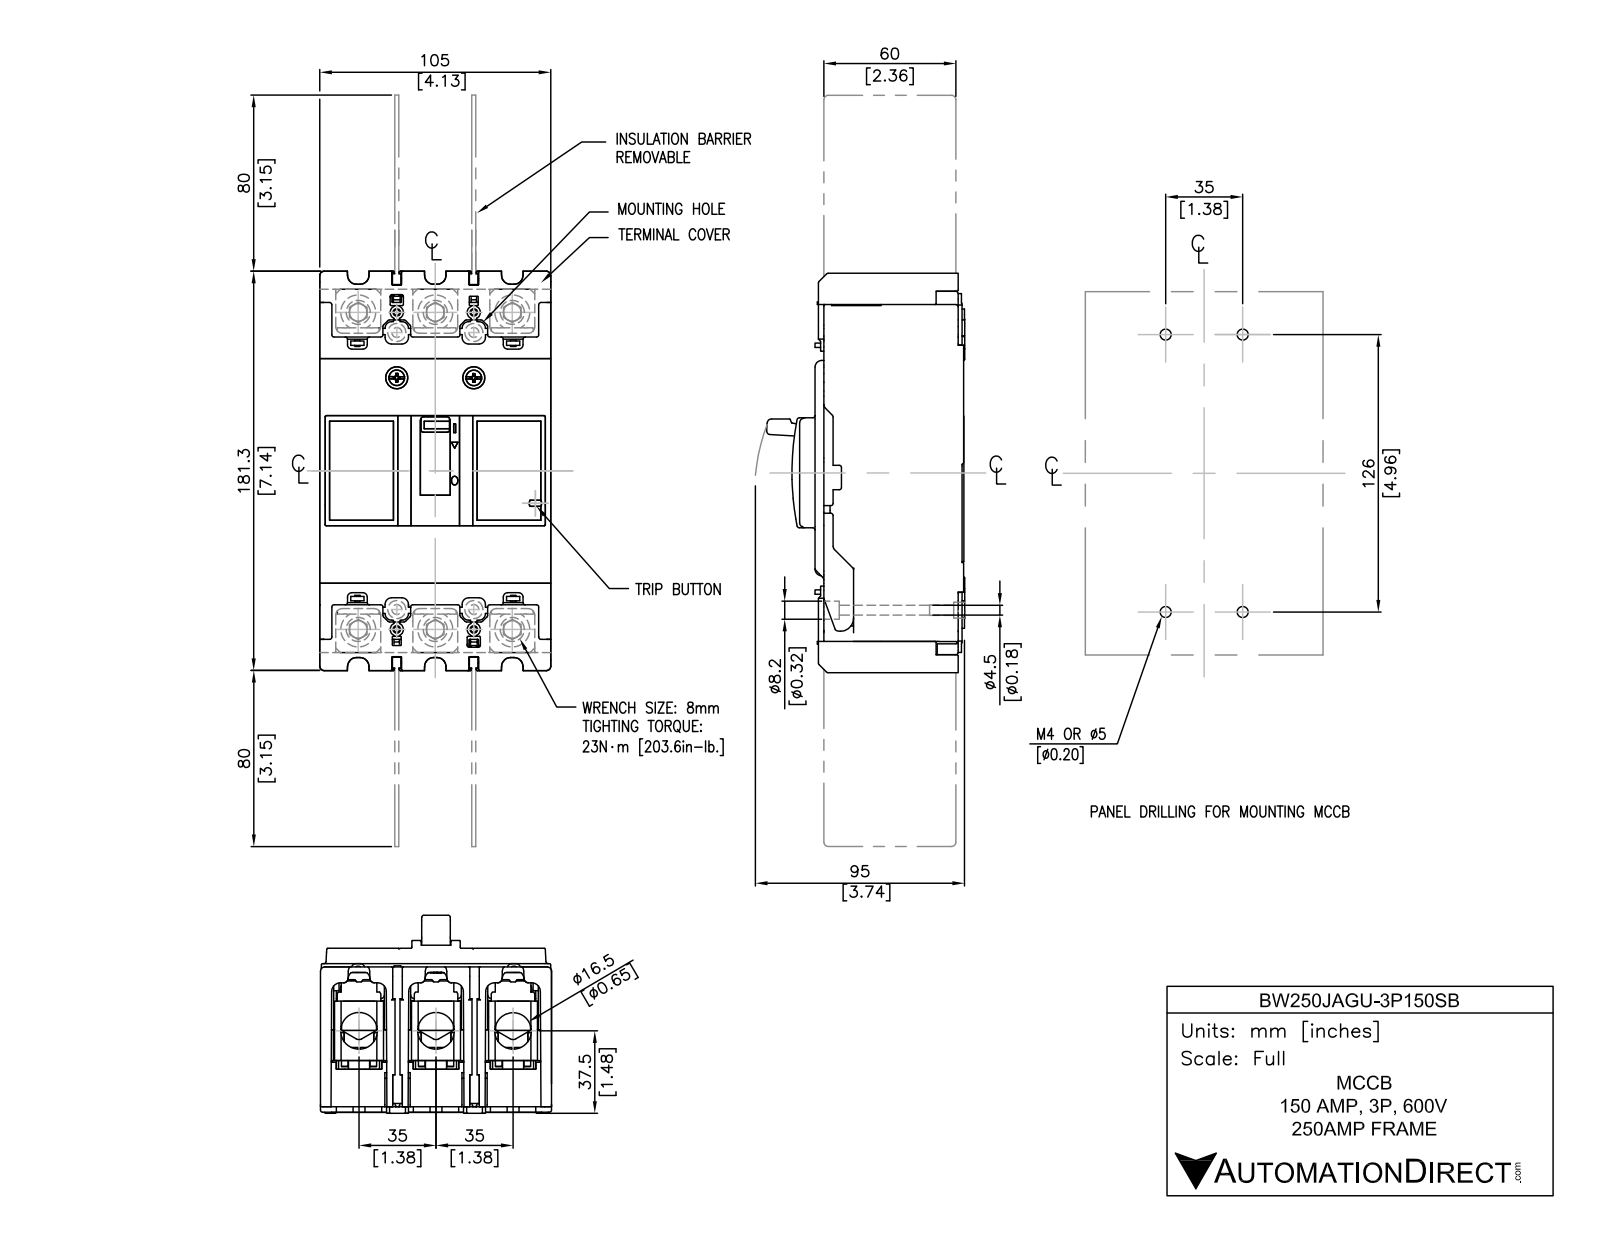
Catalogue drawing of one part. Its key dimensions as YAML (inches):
part_name: "BW250JAGU-3P150SB"
step_written_by: "SolidWorks 2018 (AUTOMOTIVE_DESIGN)"
units: inches
bodies: {solids: 10, faces: 471, planar: 338, cylindrical: 121, other: 12}
overall_size: [7.441, 4.134, 3.583]
volume: 67.56
surface_area: 224
round_holes:
  - {diameter: 0.315, count: 6}
  - {diameter: 0.177, count: 4}
  - {diameter: 0.323, count: 4}
round_bosses_or_shafts:
  - {diameter: 0.512, count: 6}
partial_cylinders:
  - {radius: 0.039, count: 36}
  - {radius: 0.118, count: 16}
  - {radius: 0.079, count: 8}
  - {radius: 0.492, count: 3}
face_to_face_distances: [0.098, 2.5, 4.134, 1.378, 0.787, 2.598, 1.24, 0.335, 0.157, 0.059]
hole_center_spacings: [0.775, 5.359, 1.378, 2.097, 5.703, 5.834, 5.669, 2.756]
